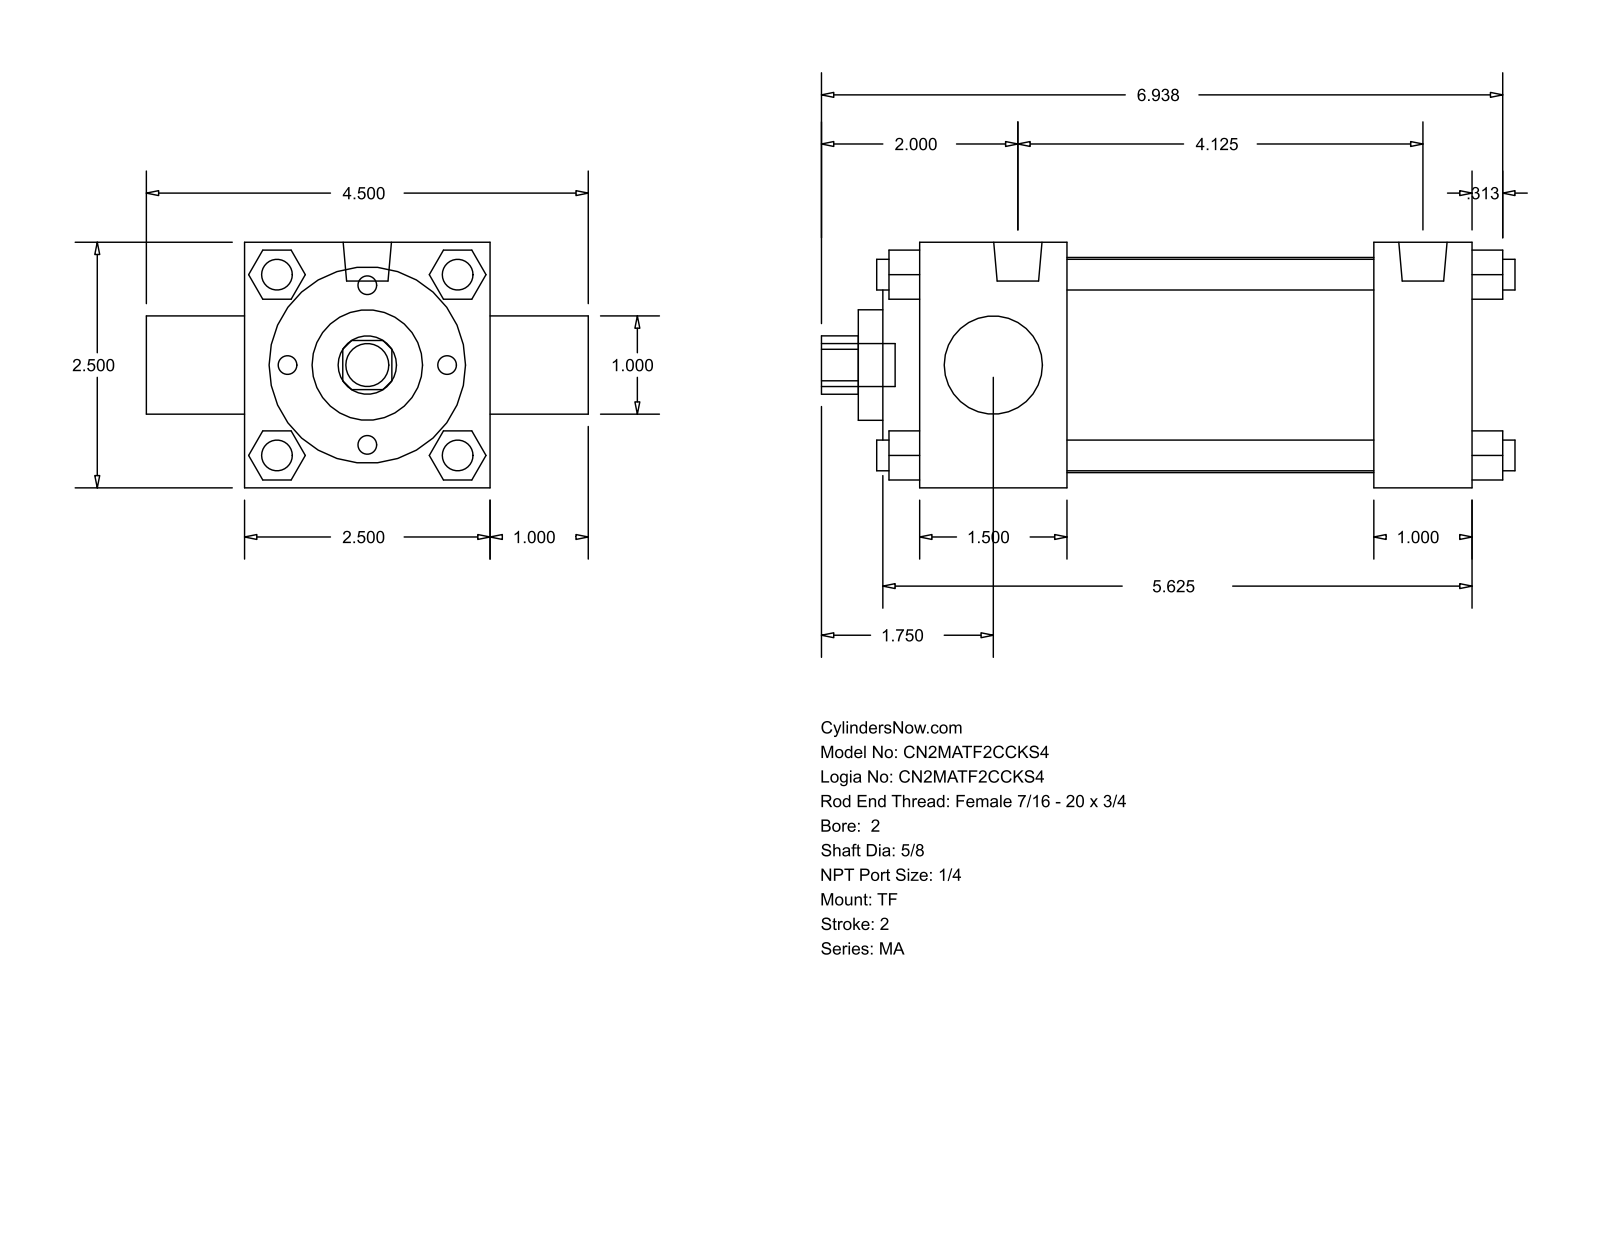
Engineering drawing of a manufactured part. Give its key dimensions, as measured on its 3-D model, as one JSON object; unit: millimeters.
{"part_name": "MA_TF__0200_0.625", "step_written_by": "GSSL Pune (CONFIG_CONTROL_DESIGN)", "units": "millimeters", "bodies": {"solids": 0, "faces": 122, "planar": 93, "cylindrical": 29, "other": 0}, "overall_size": [179.39, 114.3, 63.5], "round_holes": [[15.88, 1], [25.4, 1], [28.57, 1], [50.8, 1], [55.63, 1]], "round_bosses_or_shafts": [[7.94, 7], [12.49, 2], [11.11, 1]], "partial_cylinders_radius": [[7.54, 1]], "face_to_face_distances": [63.5, 25.4, 38.1, 12.7, 142.88, 9.52, 117.48, 79.38, 104.78, 47.62]}
